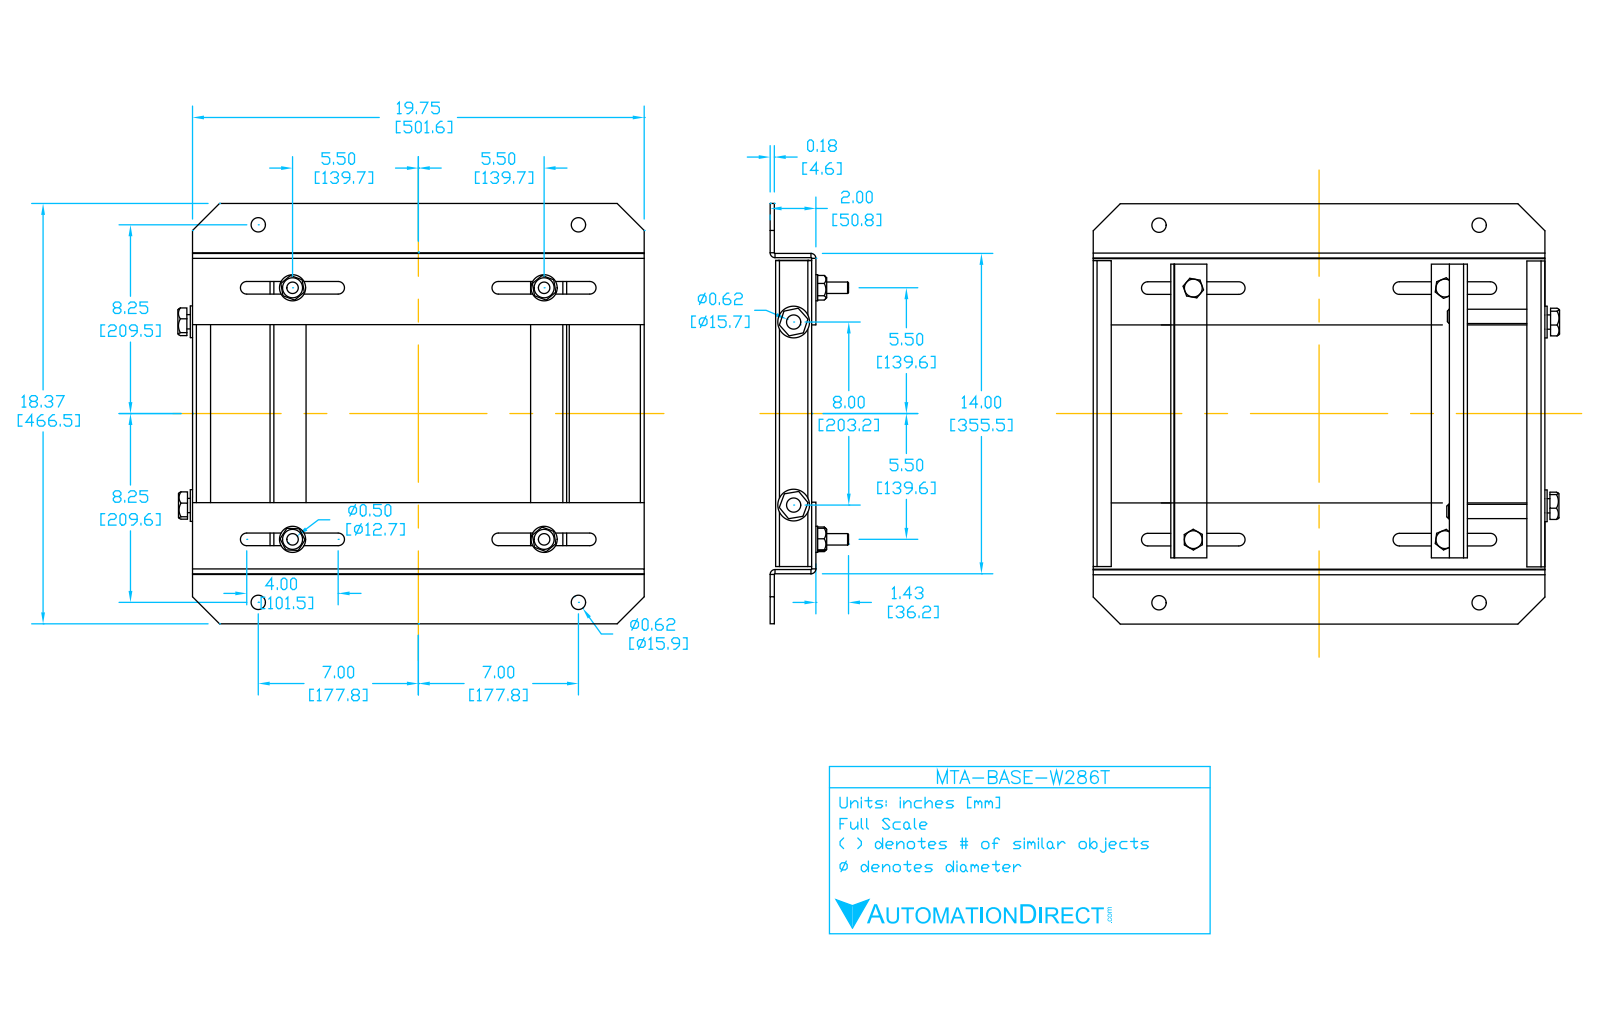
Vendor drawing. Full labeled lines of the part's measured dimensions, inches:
Part name (STEP PRODUCT): W286T
STEP written by: SolidWorks 2017 (AUTOMOTIVE_DESIGN)
Units: inches
Bodies: 26 solids, 394 faces (224 planar, 106 cylindrical, 64 other)
Overall size (bounding box): 20.163 × 18.375 × 3.697
Volume: 77.8 in³ · Surface area: 978.2 in²
Round holes (diameter × count): ⌀0.5 ×4, ⌀0.504 ×4, ⌀0.531 ×4, ⌀0.625 ×4, ⌀0.65 ×2, ⌀0.748 ×2, ⌀0.625 ×1, ⌀0.625 ×1
Round bosses / shafts (diameter × count): ⌀1.142 ×4, ⌀1.386 ×2
Partial cylindrical surfaces — rounded edges, fillets, slot ends (radius × count): R0.029 ×11, R0.289 ×8, R0.167 ×4, R0.214 ×4, R0.147 ×3
Main face-to-face distances: 0.185, 1.815, 2, 1.63, 0.118, 0.138, 13.815, 1.697, 1.457, 0.303
Hole centre spacings: 3.969, 11, 11.889, 14, 16.197, 16.5, 21.639, 2.85
